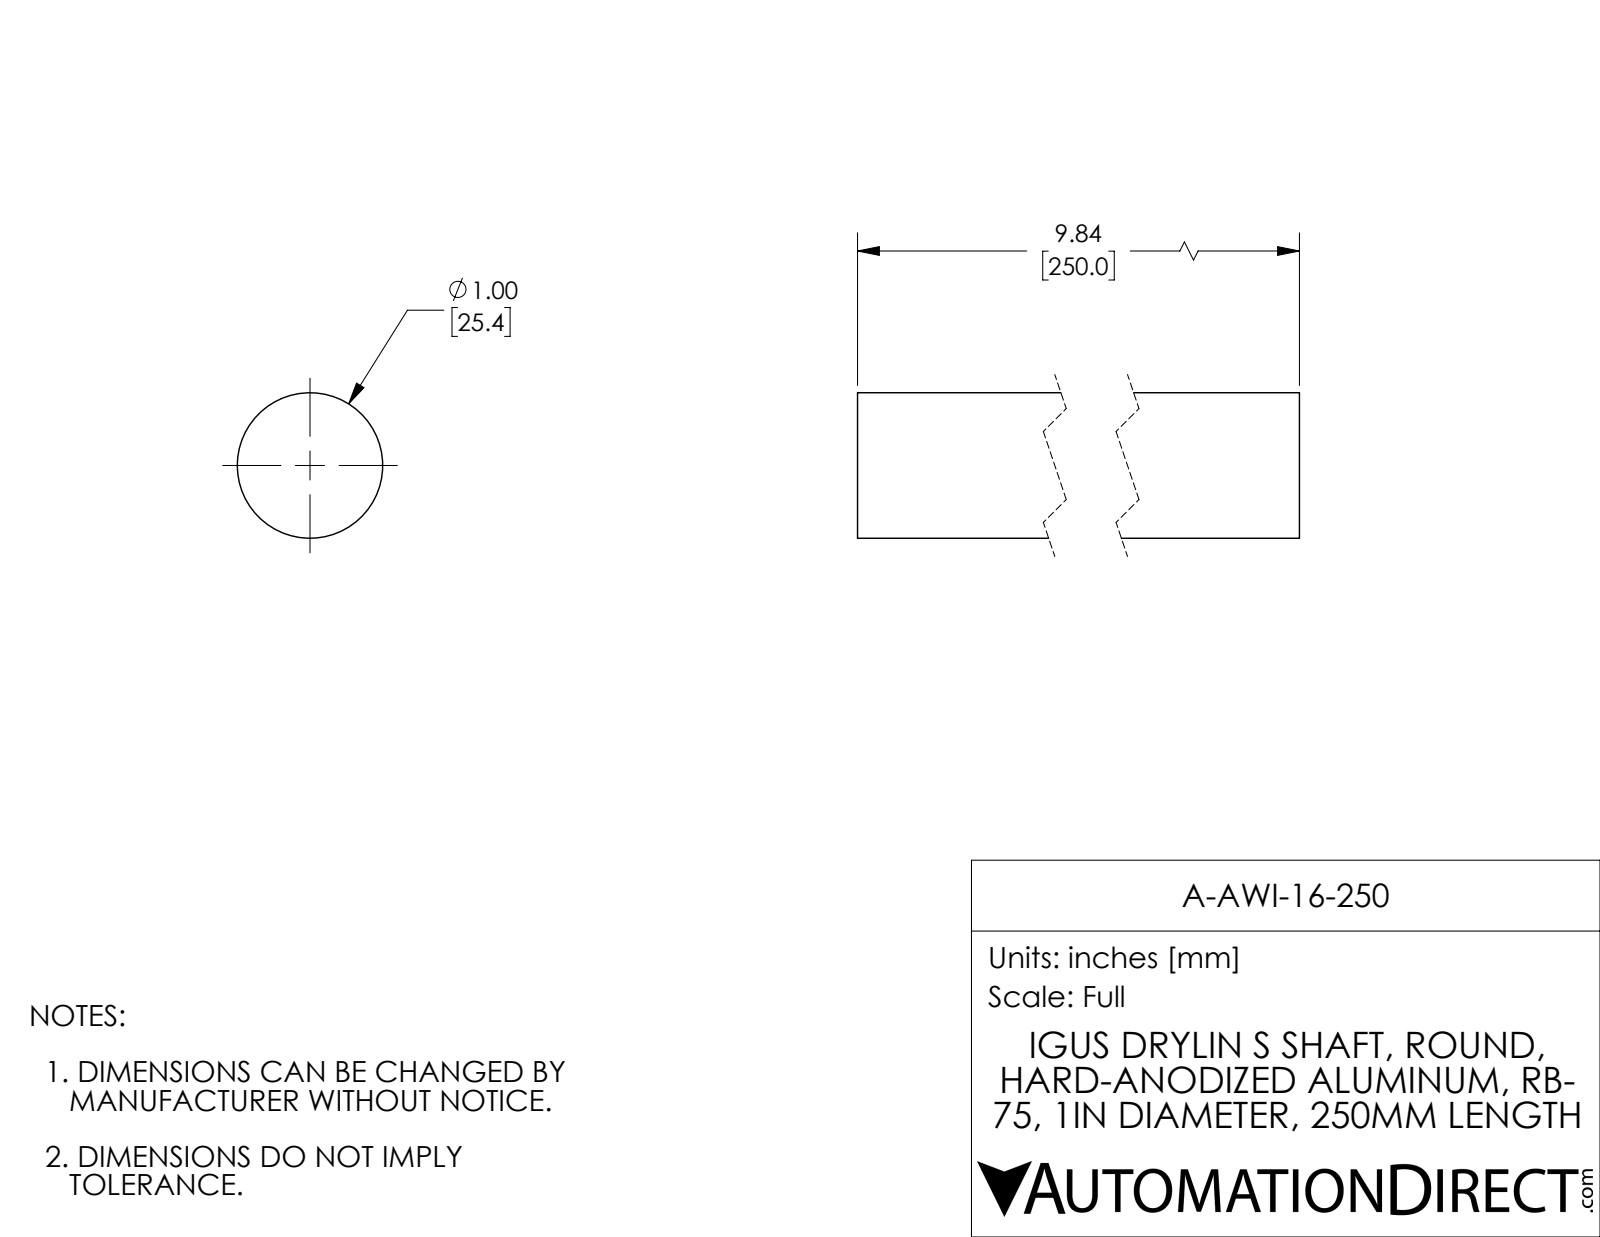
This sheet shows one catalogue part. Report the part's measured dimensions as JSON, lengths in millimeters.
{"part_name": "A-AWI-16-250", "step_written_by": "SolidWorks 2017 (AUTOMOTIVE_DESIGN)", "units": "millimeters", "bodies": {"solids": 1, "faces": 4, "planar": 2, "cylindrical": 2, "other": 0}, "overall_size": [250, 25.4, 25.4], "volume_mm3": 126700, "surface_area_mm2": 20960, "round_bosses_or_shafts": [[25.4, 1]], "face_to_face_distances": [250]}
